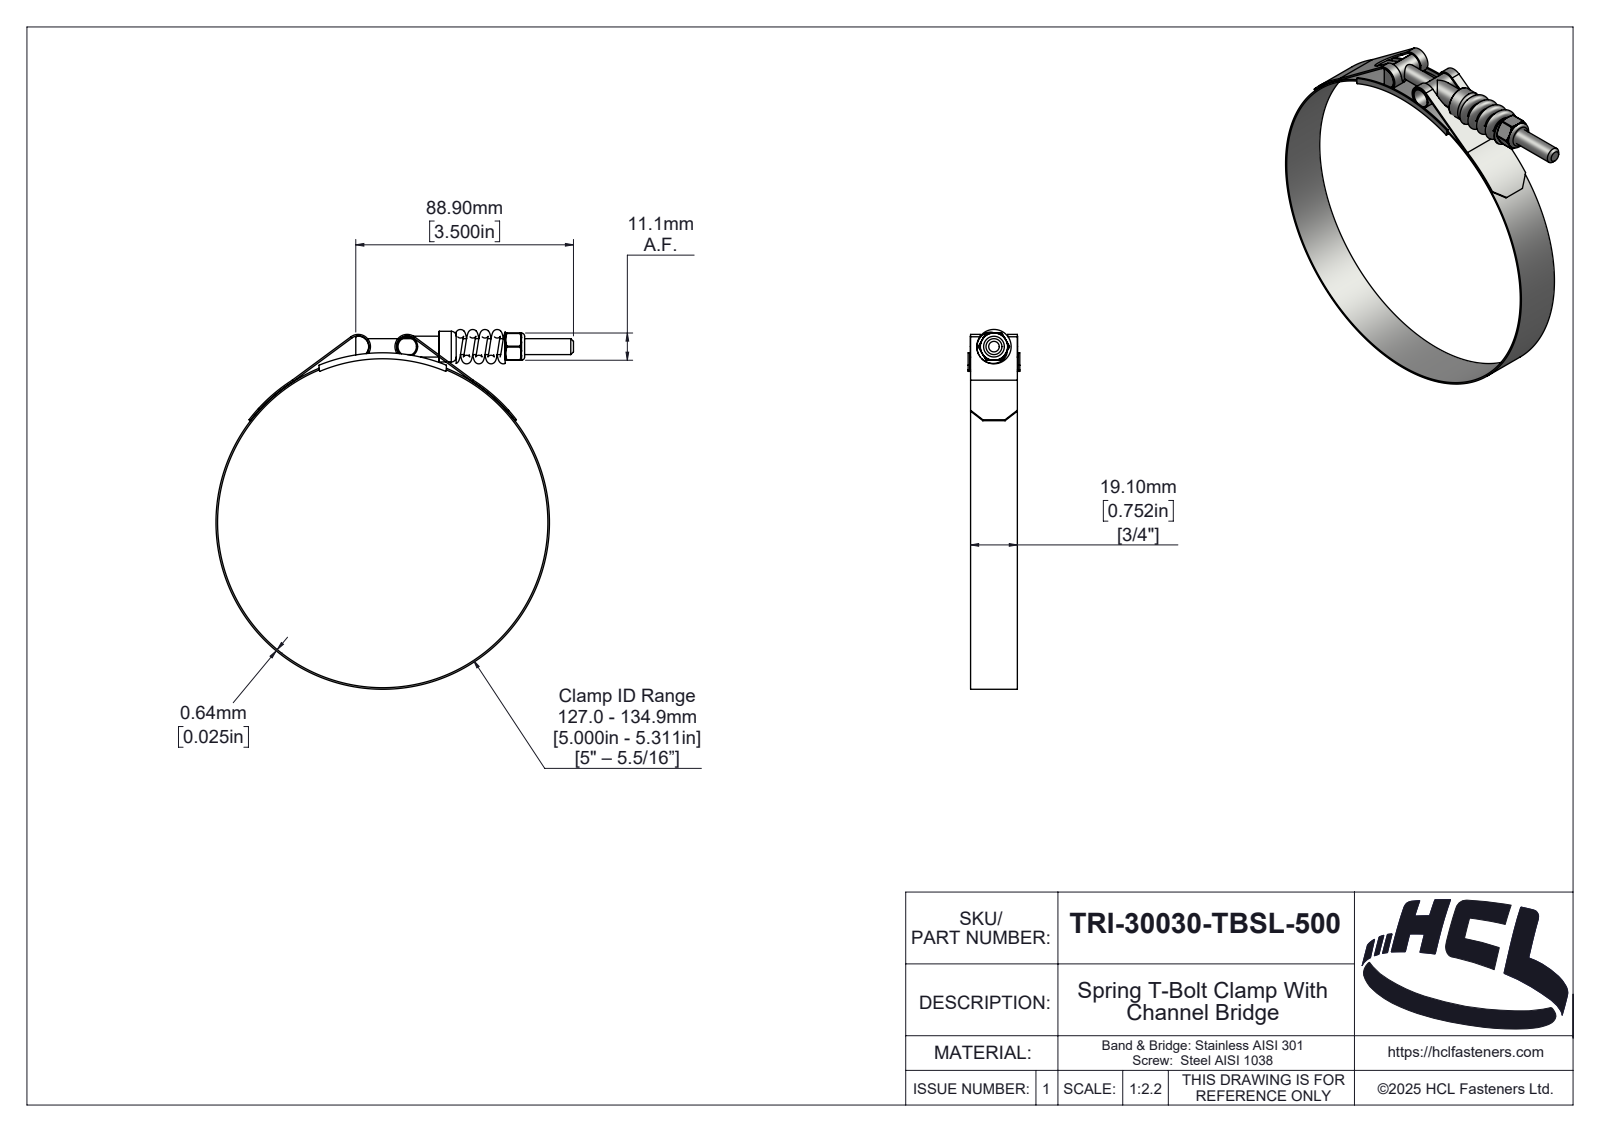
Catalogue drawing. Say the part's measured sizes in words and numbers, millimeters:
The part is named "TRI-30030-TBSL-500". Its 3-D file was written by "SolidWorks 2025 (AUTOMOTIVE_DESIGN)". It is 7 solids with 332 faces: 48 planar, 122 cylindrical and 162 other. Overall it measures 146.99 by 146.87 by 21.1 millimeters. Its volume is 13 592 cubic millimeters and its surface area 29 843 square millimeters. Round holes: 1 of diameter 5.4, 1 of diameter 6.35, 1 of diameter 6.5, 1 of diameter 7.52, 1 of diameter 134.9. Round bosses or shafts: 2 of diameter 8.52, 1 of diameter 136.18, 1 of diameter 12.52. Partial cylindrical surfaces (rounded edges, fillets, slot ends): 6 of radius 0.39, 2 of radius 0.5, 2 of radius 4.36, 2 of radius 5, 1 of radius 0.59, 1 of radius 2.42, 1 of radius 3.03, 1 of radius 3.19. The main face-to-face distances are 0.64, 19.1, 1, 20.1, 20.46, 0.36, 19.46, 21.1, 61, 11.11. The hole center spacings are 72.45.
